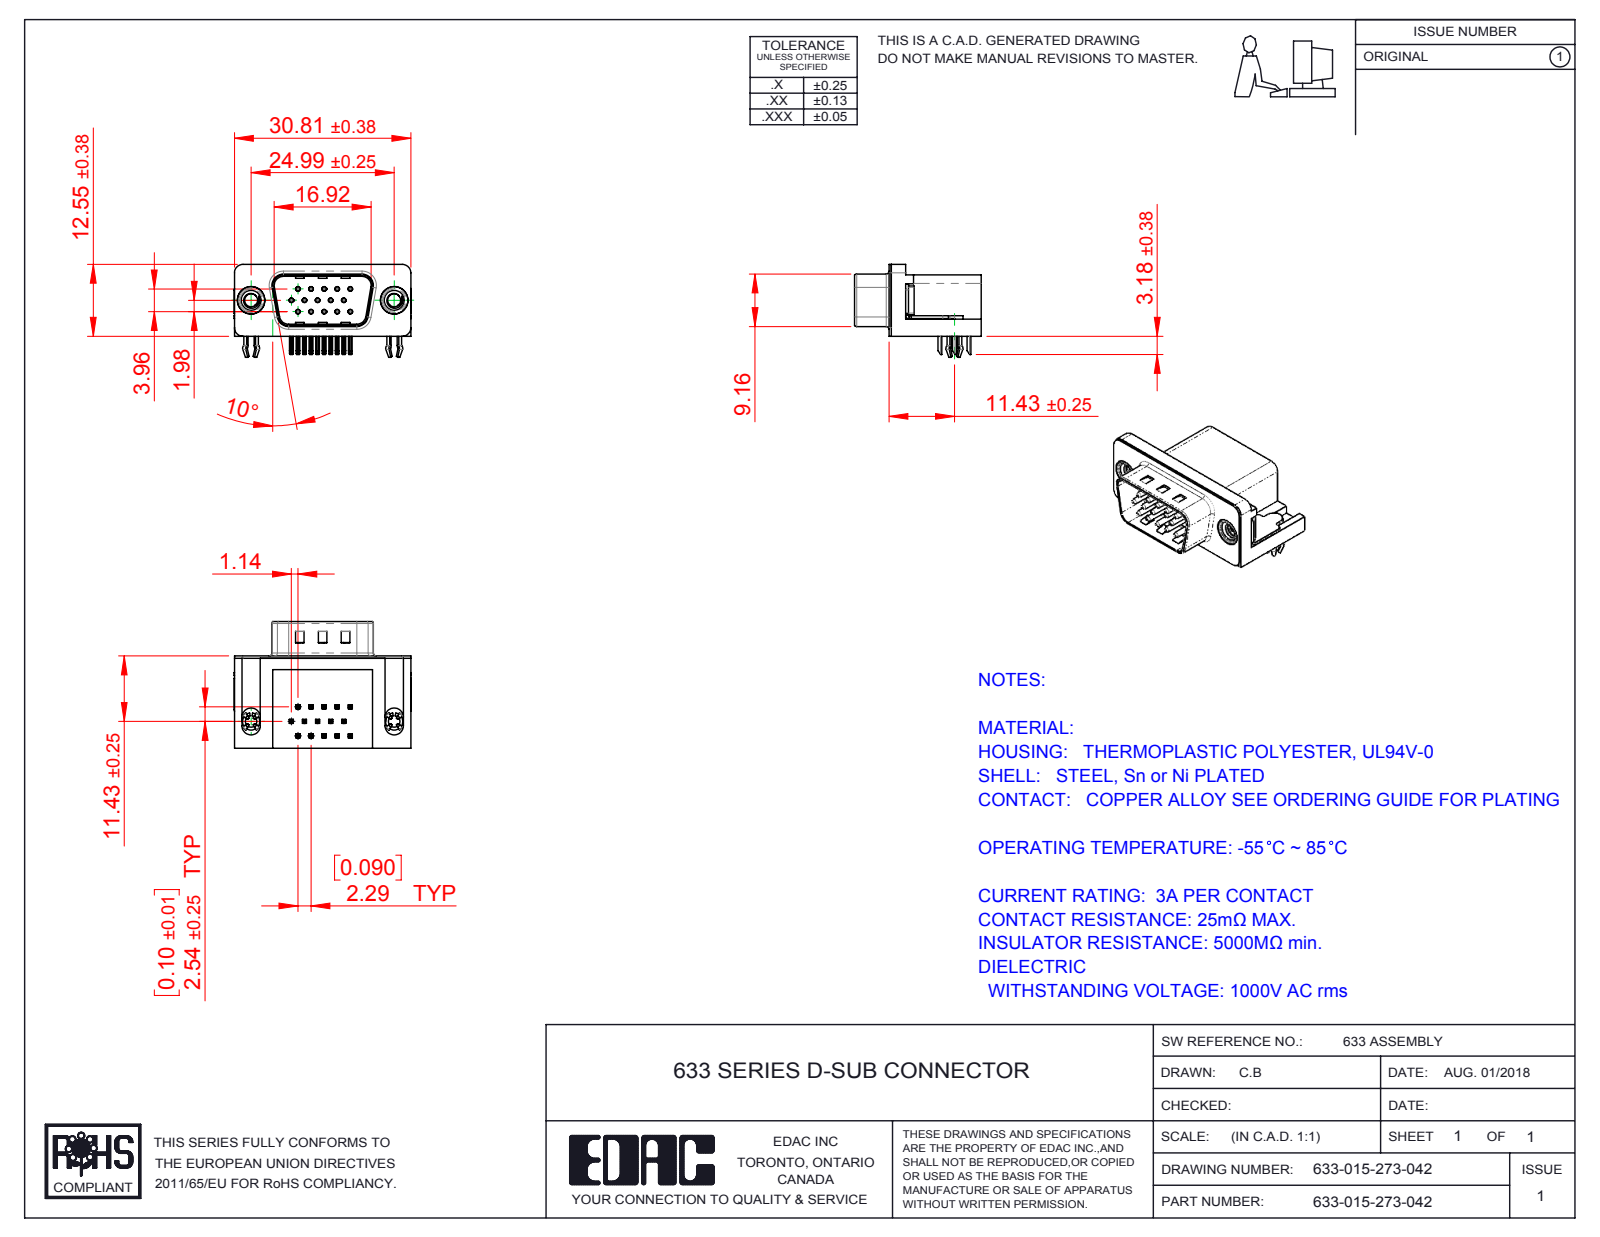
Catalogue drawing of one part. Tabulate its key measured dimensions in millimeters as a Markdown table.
| quantity | value |
| --- | --- |
| part name | 633 4-40 Threaded Rivet; 633 Contact Middle; 633 4 Prong Board Lock; 633 Contact Middle_Recessed (+5 more) |
| STEP written by | SolidWorks 2016 (CONFIG_CONTROL_DESIGN) |
| units | millimeters |
| bodies | 21 solids, 1563 faces (903 planar, 449 cylindrical, 211 other) |
| overall size | 30.89 × 22.1 × 16.25 |
| volume | 4 084 mm³ |
| surface area | 5 496 mm² |
| round holes (diameter × count) | 0.35 × 15, 0.8 × 15, 2 × 2, 2.26 × 2, 4 × 2, 4.8 × 2, 5 × 2 |
| round bosses / shafts (diameter × count) | 0.75 × 15, 4.9 × 2, 4.75 × 2, 3.9 × 2, 3 × 2 |
| partial cylindrical surfaces (radius × count) | 0.25 × 72, 0.12 × 30, 1 × 16, 0.5 × 9, 1.6 × 8, 1.5 × 7, 0.9 × 4, 2 × 4 |
| main face-to-face distances | 0.4, 10.35, 15.7, 2.9, 6.7, 16.1, 2.5, 0.5, 0.35, 10.7 |
| hole center spacings | 3.96, 2.28, 4.57, 2.29, 6.05, 6.86, 7.92, 6.04 |
